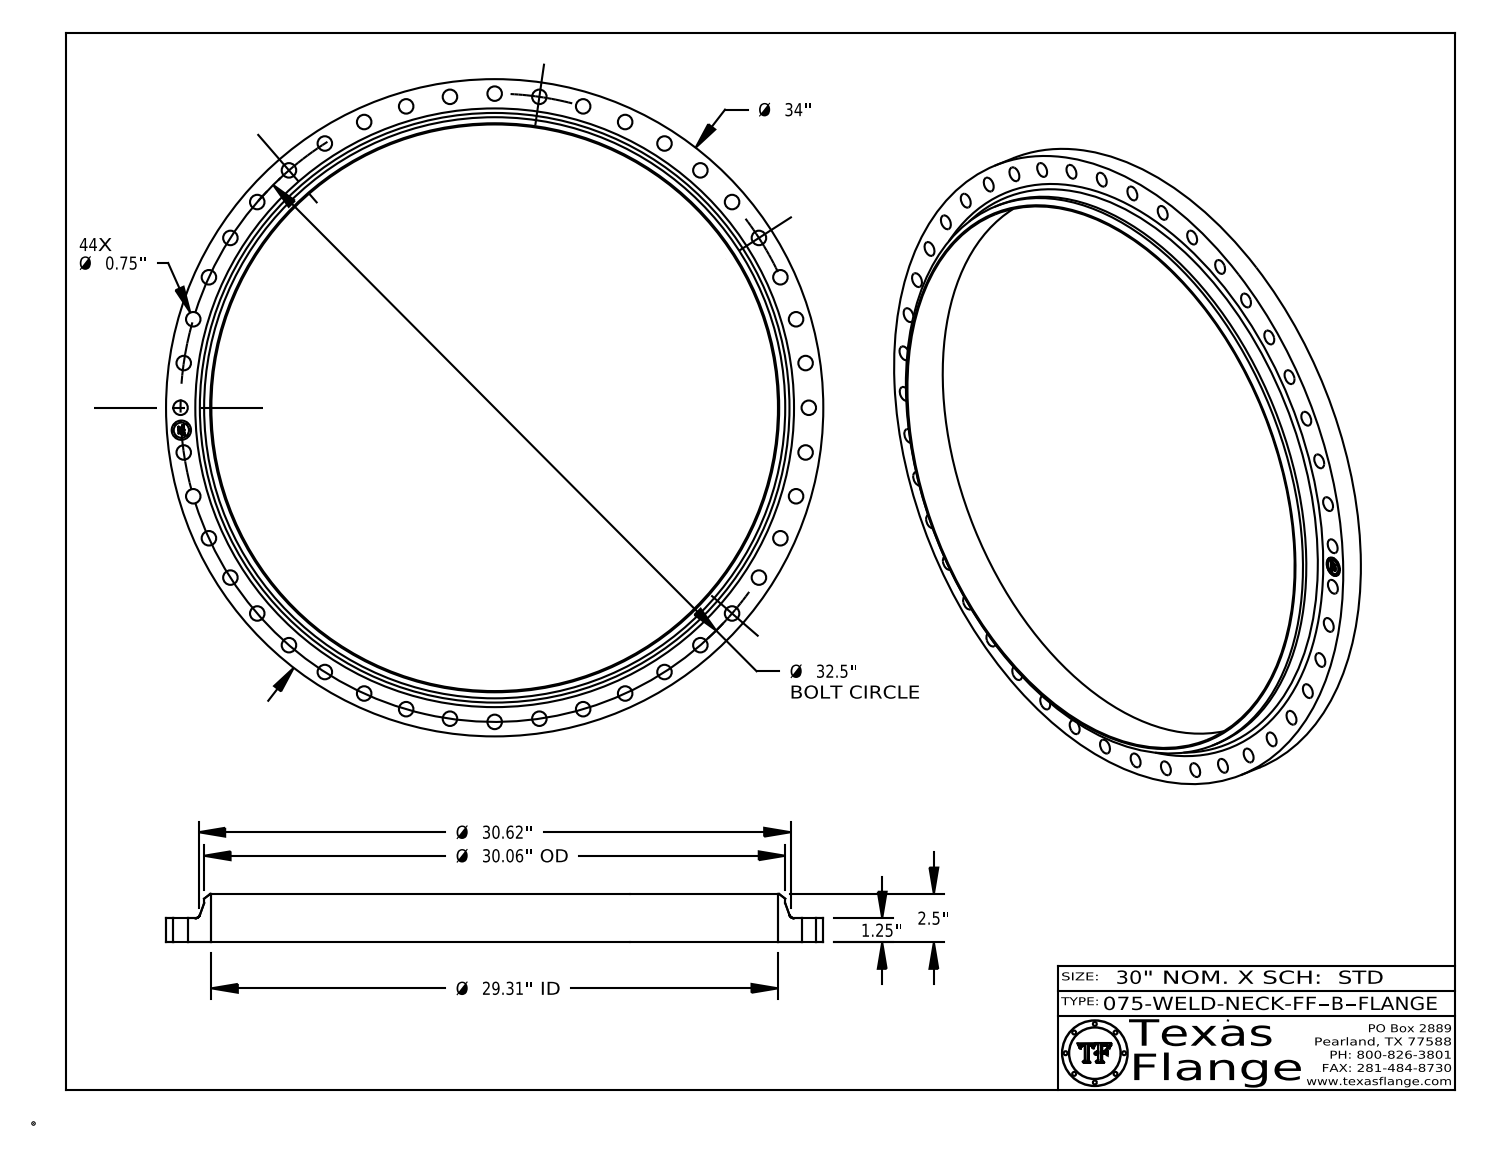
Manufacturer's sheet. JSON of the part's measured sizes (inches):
{"part_name": "075-WELD-NECK-FF, Series B", "step_written_by": "CATIA V5 STEP AP214 (AUTOMOTIVE_DESIGN)", "units": "inches", "bodies": {"solids": 1, "faces": 488, "planar": 368, "cylindrical": 114, "other": 6}, "overall_size": [34, 34, 2.5], "volume_in3": 318.2, "surface_area_in2": 998.4, "round_holes": [[0.75, 44], [1, 1], [29.31, 1]], "round_bosses_or_shafts": [[0.061, 8], [34, 1], [30.06, 1], [0.788, 1]], "face_to_face_distances": [1.25, 2.5, 1.235, 0.015, 1.265, 0.298, 0.292, 0.054, 0.193, 0.248], "hole_center_spacings": [16.25, 32.417, 32.169, 31.183, 9.156, 4.625, 29.563, 31.757]}
